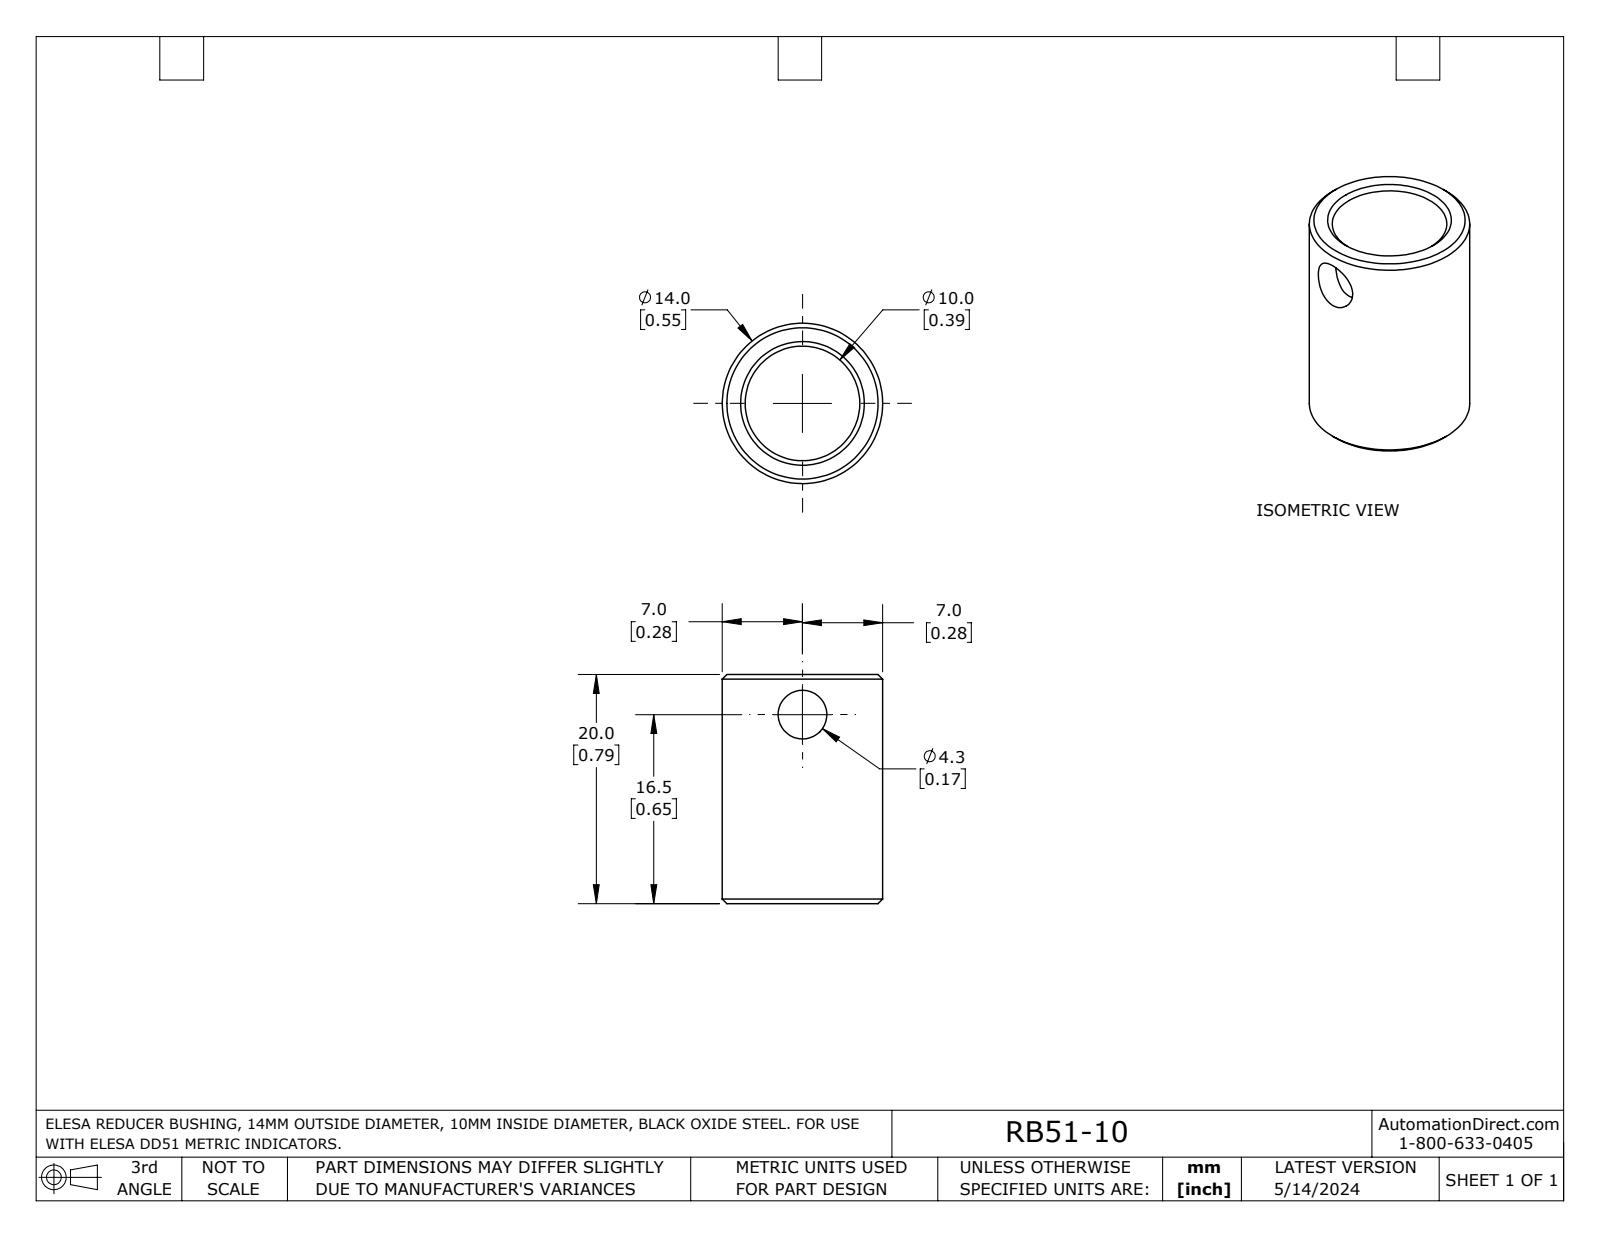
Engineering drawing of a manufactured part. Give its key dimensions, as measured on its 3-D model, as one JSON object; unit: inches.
{"part_name": "RB51-10", "step_written_by": "SolidWorks 2023 (AUTOMOTIVE_DESIGN)", "units": "inches", "bodies": {"solids": 1, "faces": 9, "planar": 2, "cylindrical": 3, "other": 4}, "overall_size": [0.787, 0.551, 0.551], "volume_in3": 0.09, "surface_area_in2": 2.514, "round_holes": [[0.167, 1], [0.394, 1]], "round_bosses_or_shafts": [[0.551, 1]], "face_to_face_distances": [0.787]}
